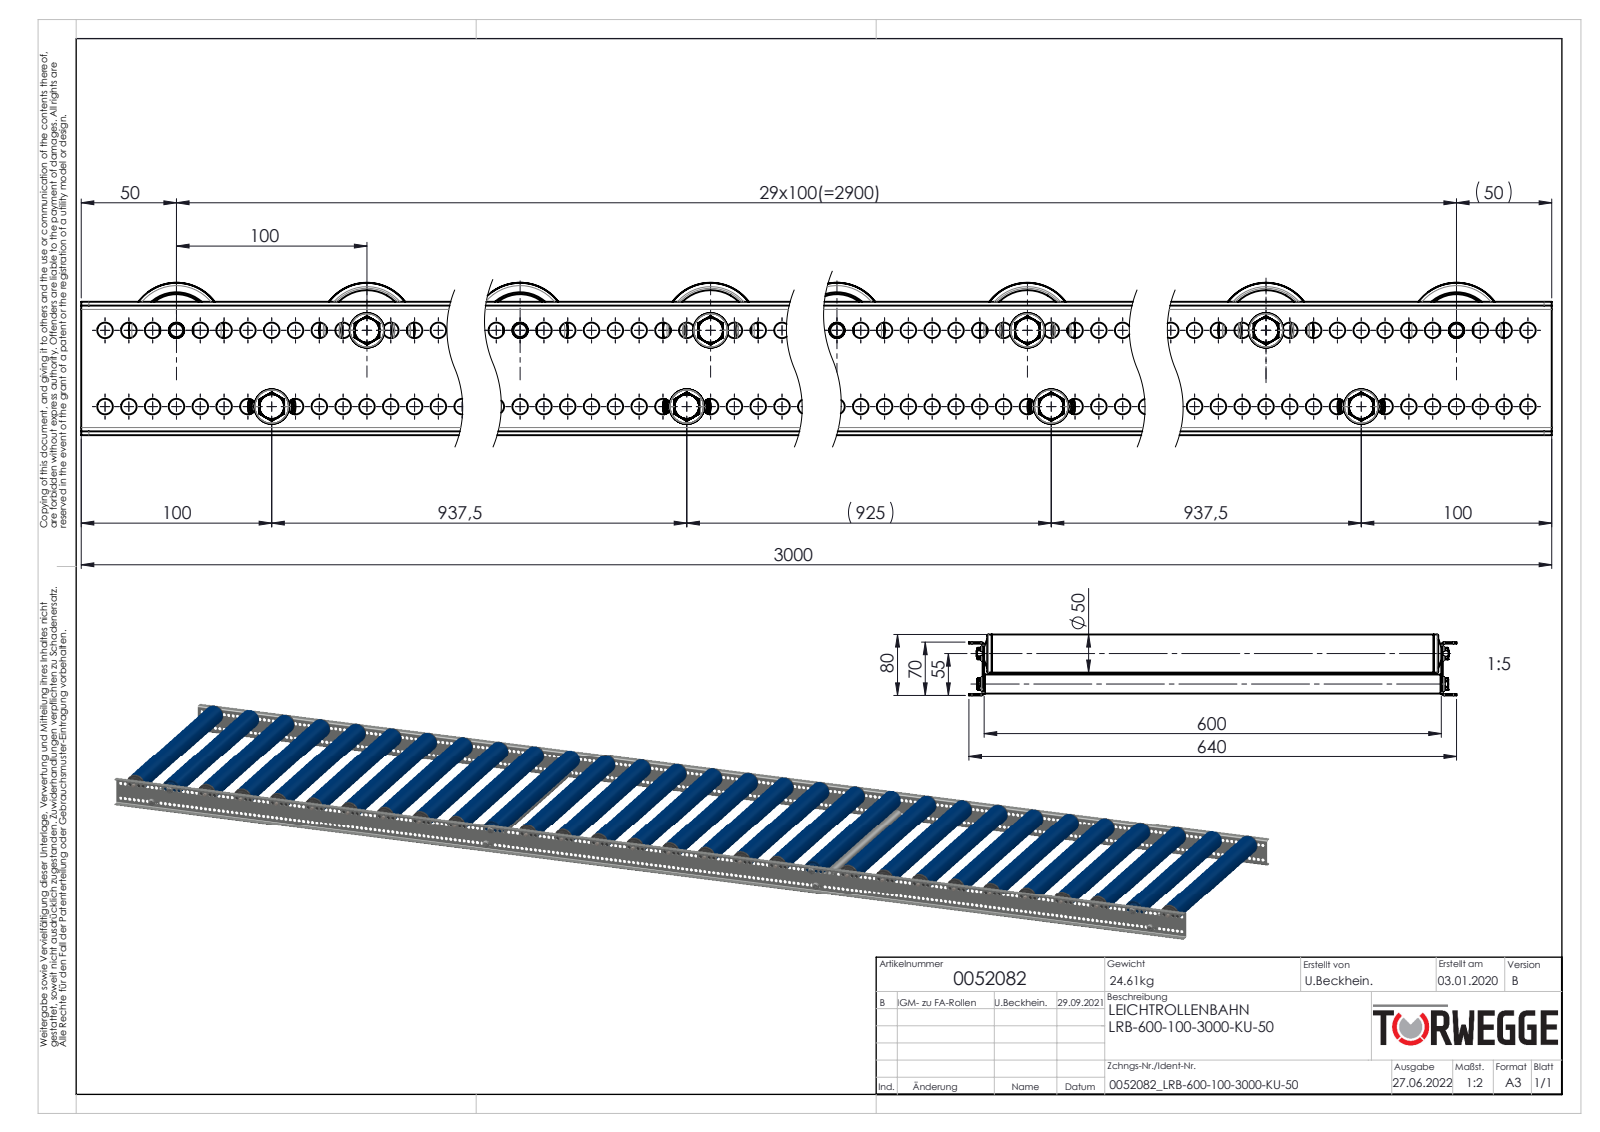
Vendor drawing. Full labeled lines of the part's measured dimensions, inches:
Part name (STEP PRODUCT): 0017015_Tragrollenrohr-Ø50x2,8KU_KFG_0017015_L=585; 0017015_Tragrollenrohr-Ø50x2,8KU_KFG_L=580; 0039778-Achse-ST-Ø08-KFG_AL620-G; KUT100-50x2,8-KB-A8-FA_KFG_0034516_KUT100-50x2,8-KB-A8-FA-EL=600 (+8 more)
STEP written by: SolidWorks 2020 (AUTOMOTIVE_DESIGN)
Units: inches
Bodies: 529 solids, 10474 faces (2574 planar, 4860 cylindrical, 3040 other)
Overall size (bounding box): 118.11 × 25.197 × 3.15
Volume: 706 in³ · Surface area: 13 340 in²
Round holes (diameter × count): ⌀0.323 ×478, ⌀0.299 ×26, ⌀0.315 ×26, ⌀0.984 ×26, ⌀1.181 ×26, ⌀1.378 ×26, ⌀1.551 ×26, ⌀1.575 ×26, ⌀0.268 ×8, ⌀0.472 ×4, ⌀0.476 ×4, ⌀0.63 ×4
Round bosses / shafts (diameter × count): ⌀1.969 ×30, ⌀1.748 ×26, ⌀1.496 ×26, ⌀1.417 ×26, ⌀1.299 ×26, ⌀0.866 ×26, ⌀0.827 ×26, ⌀0.984 ×8
Partial cylindrical surfaces — rounded edges, fillets, slot ends (radius × count): R0.024 ×52, R0.03 ×52, R0.096 ×52, R0.192 ×26, R0.276 ×26, R0.098 ×16, R0.157 ×8, R0.079 ×4
Main face-to-face distances: 0.079, 23.701, 2.677, 23.622, 23.78, 2.756, 2.598, 23.307, 0.236, 0.472
Hole centre spacings: 0.492, 0.984, 1.476, 1.969, 2.461, 2.953, 3.445, 3.937
